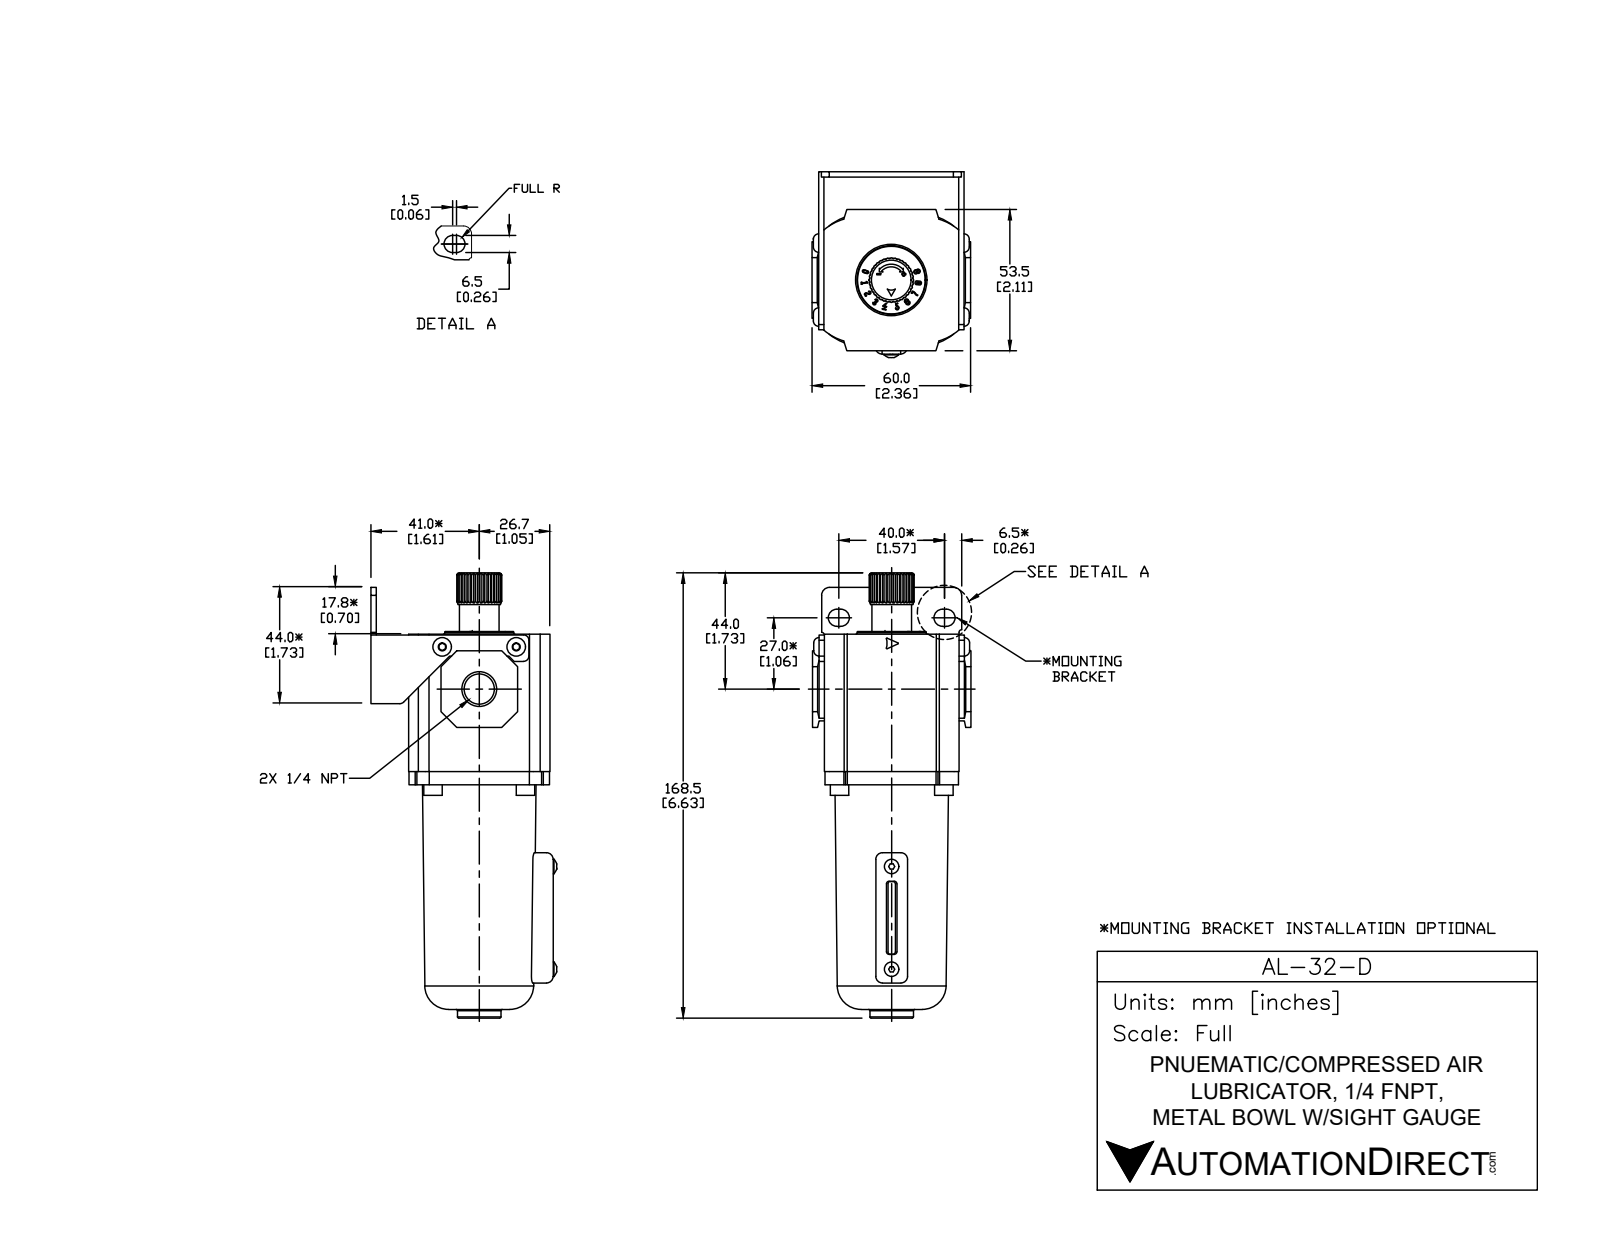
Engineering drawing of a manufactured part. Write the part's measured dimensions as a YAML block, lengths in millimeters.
part_name: "AL-32-D"
step_written_by: "SolidWorks 2015 (CONFIG_CONTROL_DESIGN)"
units: millimeters
bodies: {solids: 7, faces: 575, planar: 335, cylindrical: 110, other: 130}
overall_size: [168.5, 71, 60]
volume: 279039
surface_area: 47357
round_holes:
  - {diameter: 3.4, count: 2}
  - {diameter: 11.13, count: 1}
round_bosses_or_shafts:
  - {diameter: 7, count: 4}
  - {diameter: 5.5, count: 2}
  - {diameter: 26, count: 1}
  - {diameter: 16.5, count: 1}
  - {diameter: 15, count: 1}
partial_cylinders:
  - {radius: 1.3, count: 8}
  - {radius: 2.5, count: 8}
  - {radius: 2, count: 5}
  - {radius: 0.3, count: 4}
  - {radius: 1, count: 4}
  - {radius: 3.25, count: 4}
  - {radius: 19.9, count: 4}
  - {radius: 20, count: 4}
face_to_face_distances: [2, 53, 52, 53.4, 12.3, 14.3, 67.7, 65.7, 51, 2.5]
hole_center_spacings: [21.06, 21.46, 28]
